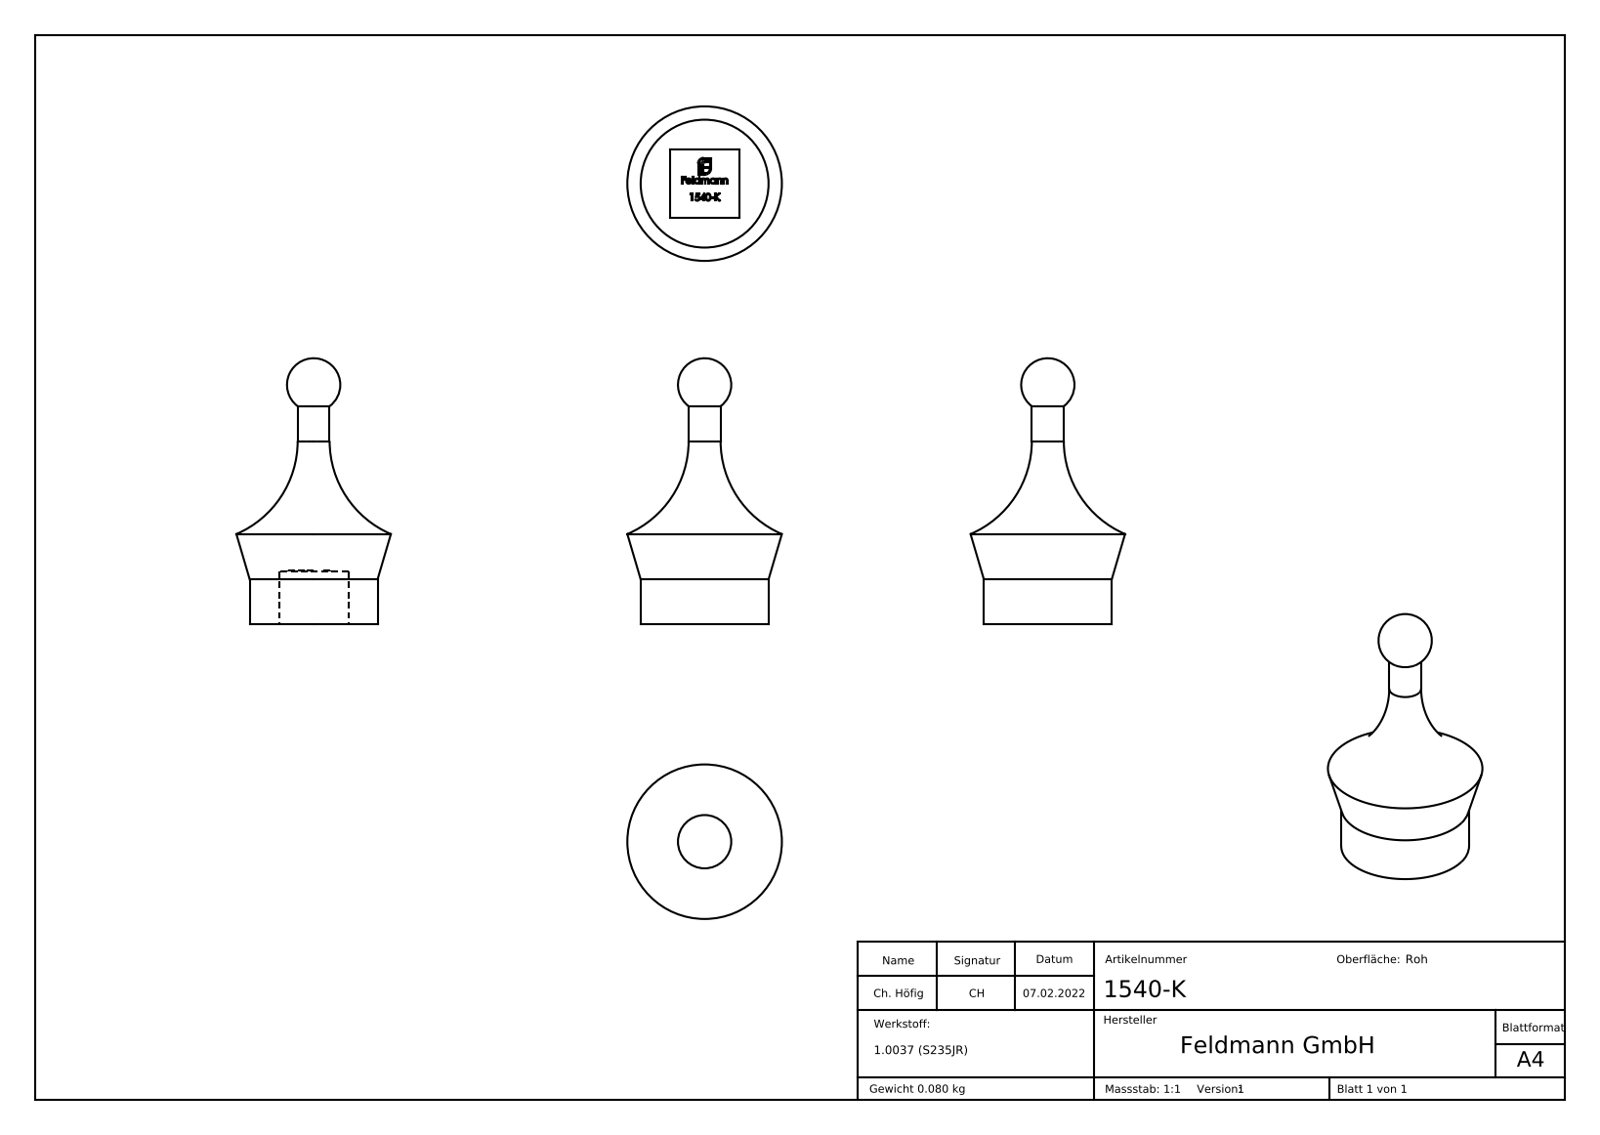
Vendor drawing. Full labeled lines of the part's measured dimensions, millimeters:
Part name (STEP PRODUCT): 1540-K
STEP written by: SolidWorks 2018 (CONFIG_CONTROL_DESIGN)
Units: millimetres
Bodies: 1 solid, 237 faces (142 planar, 4 cylindrical, 91 other)
Overall size (bounding box): 50 × 29 × 29
Volume: 10 205 mm³ · Surface area: 3 743 mm²
Round bosses / shafts (diameter × count): ⌀24 ×1, ⌀6 ×1
Main face-to-face distances: 13, 10, 10.1, 4.23, 1.14, 2.21, 3.66, 4.07, 3.34, 0.89
